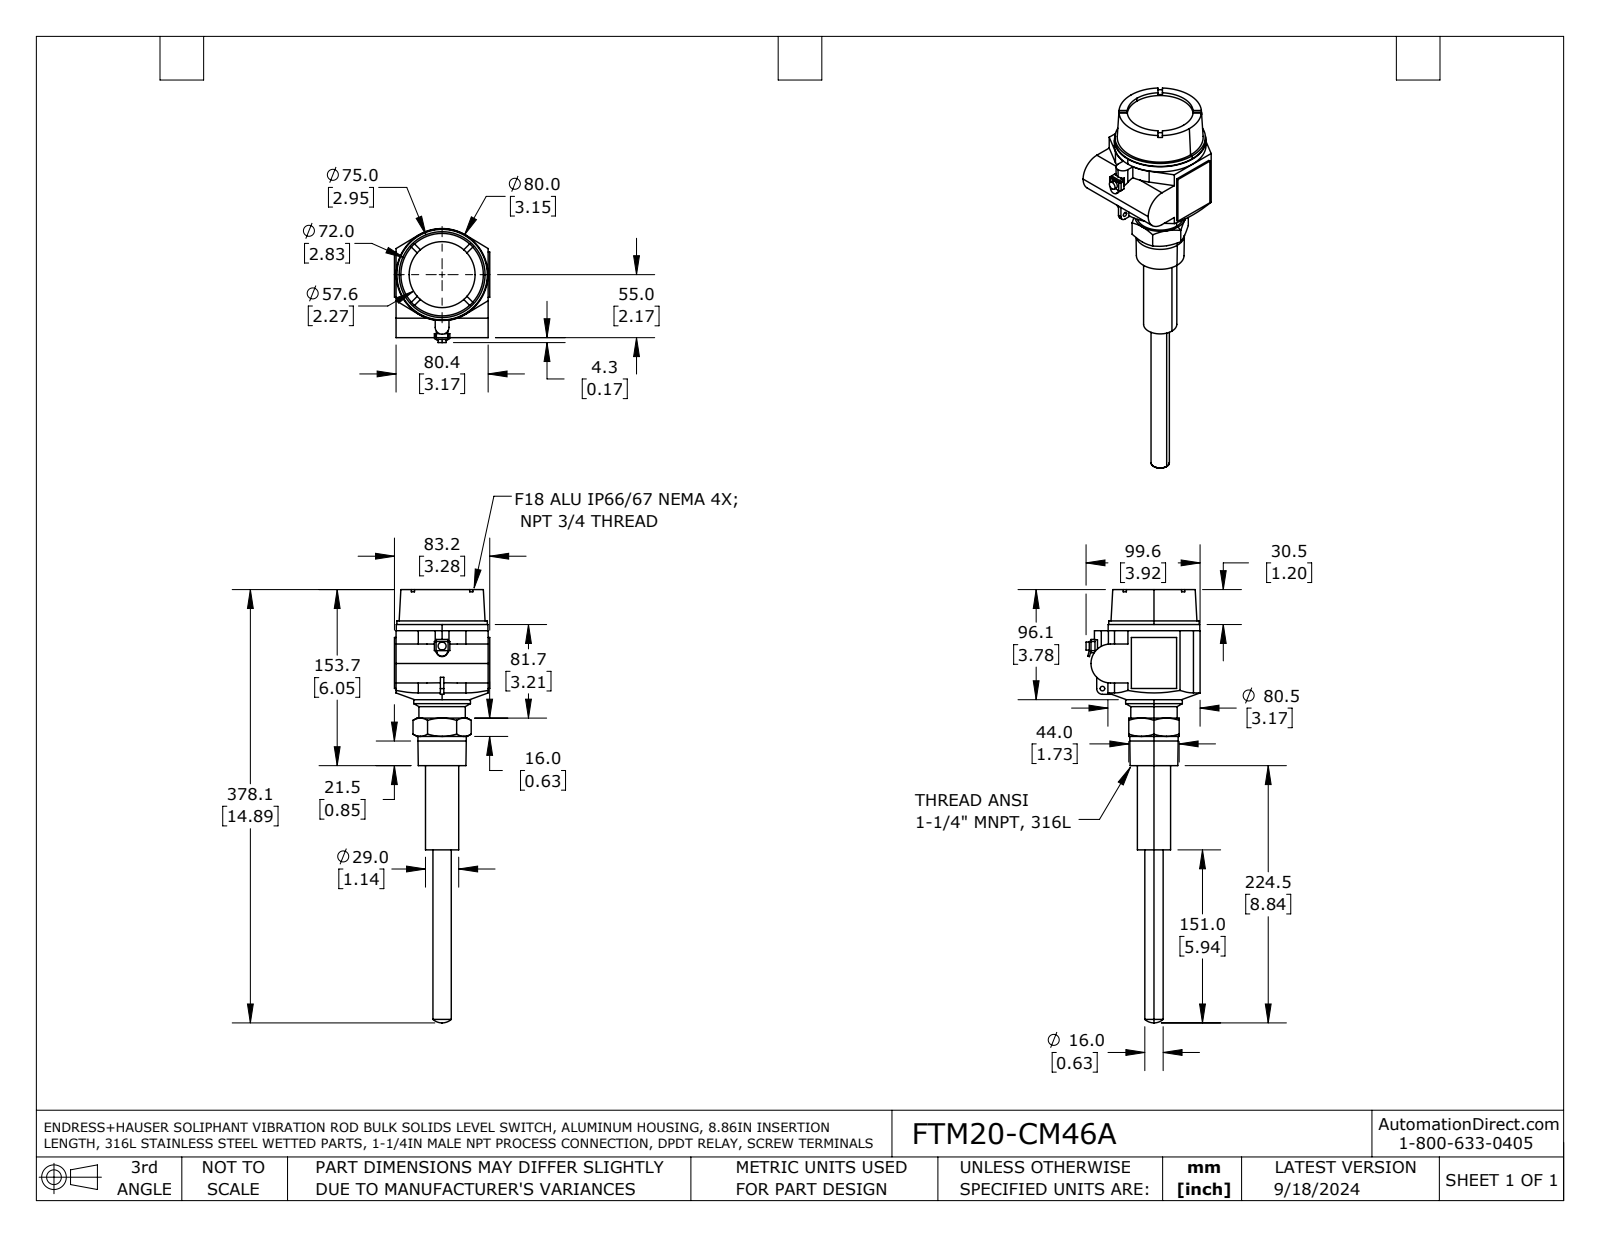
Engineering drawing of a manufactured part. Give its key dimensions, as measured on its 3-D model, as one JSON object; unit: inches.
{"part_name": "FTM20-CM46A", "step_written_by": "SolidWorks 2021 (AUTOMOTIVE_DESIGN)", "units": "inches", "bodies": {"solids": 1, "faces": 151, "planar": 88, "cylindrical": 36, "other": 27}, "overall_size": [14.888, 3.919, 3.276], "volume_in3": 41.75, "surface_area_in2": 96.75, "round_holes": [[0.157, 1], [2.268, 1]], "round_bosses_or_shafts": [[3.15, 1], [3.11, 1], [1.949, 1], [1.661, 1], [1.594, 1], [1.142, 1], [0.63, 1], [0.276, 1]], "partial_cylinders_radius": [[0.059, 3], [0.197, 2], [0.236, 1], [0.669, 1], [1.585, 1]], "face_to_face_distances": [0.055, 3.22, 3.276, 3.165, 0.118, 1.732, 3.169, 5.931, 6.049, 4.636]}
